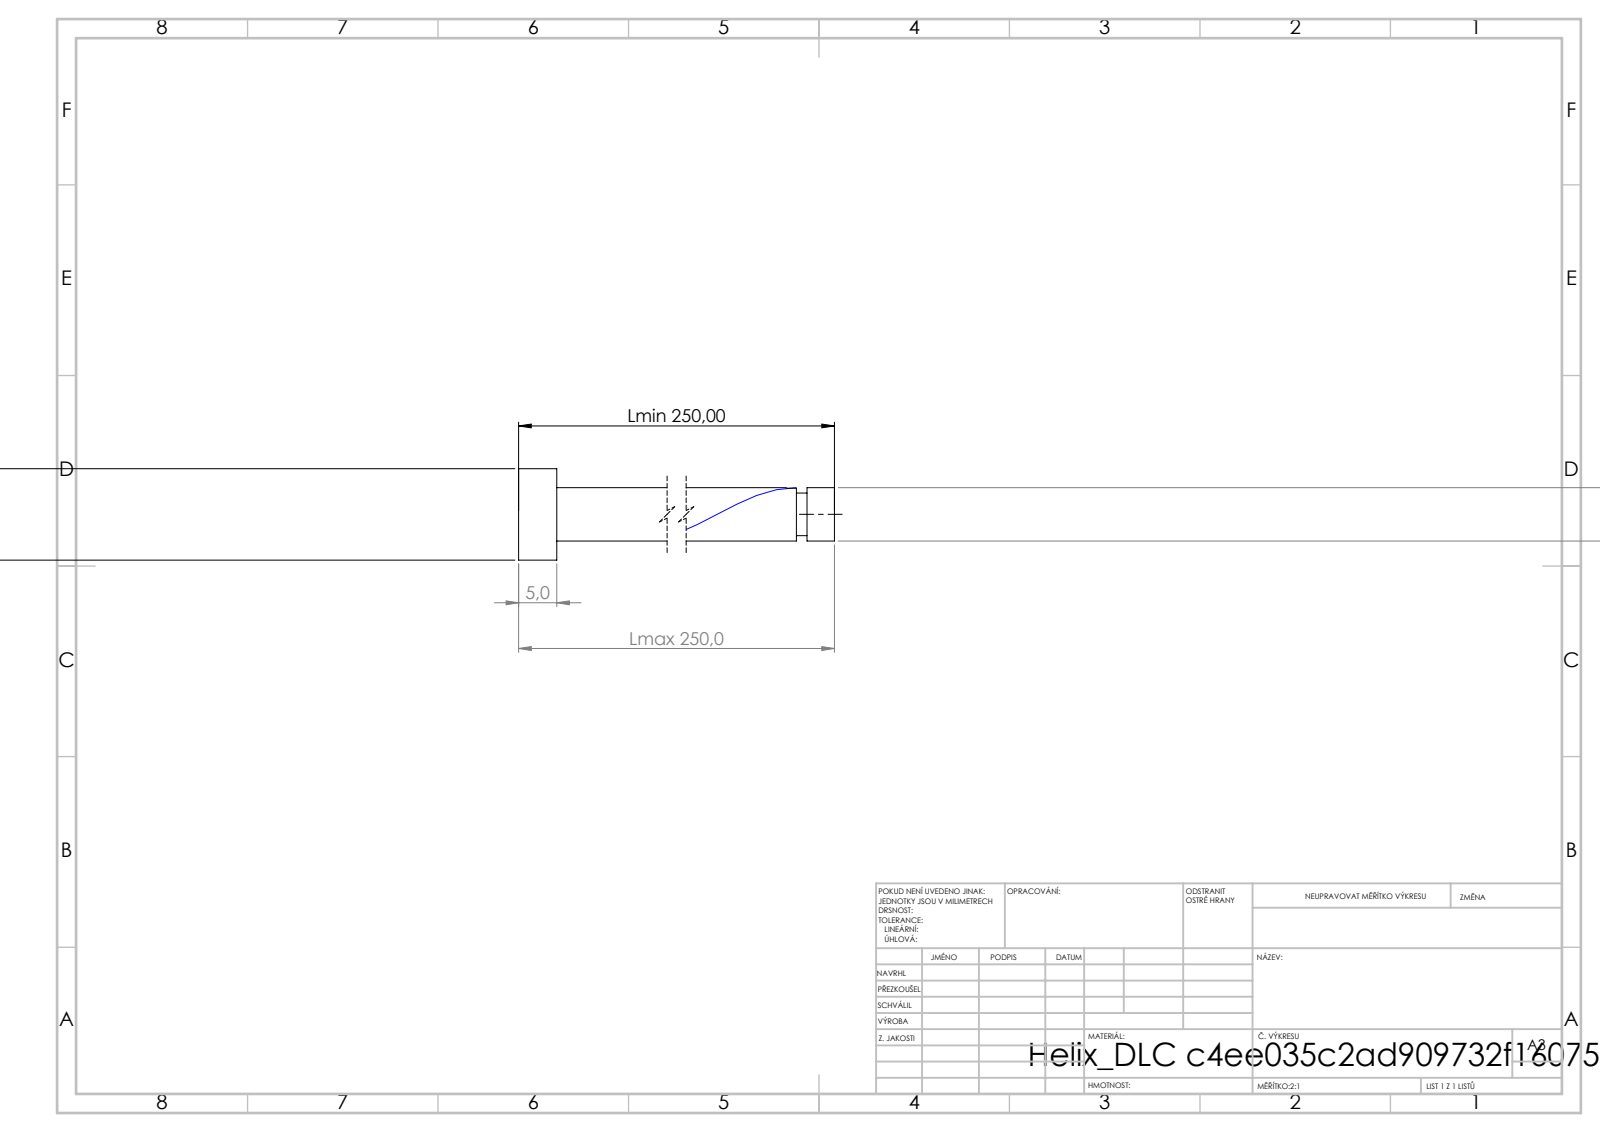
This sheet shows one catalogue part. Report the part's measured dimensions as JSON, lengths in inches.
{"step_written_by": "SolidWorks 2019 (CONFIG_CONTROL_DESIGN)", "units": "inches", "bodies": {"solids": 1, "faces": 21, "planar": 6, "cylindrical": 14, "other": 1}, "overall_size": [9.843, 0.472, 0.472], "volume_in3": 0.603, "surface_area_in2": 9.179, "round_bosses_or_shafts": [[0.472, 1], [0.276, 1], [0.22, 1]], "face_to_face_distances": [0.197, 9.646, 9.843, 9.701, 9.504, 0.142, 9.449, 0.055, 4.724, 4.528]}
